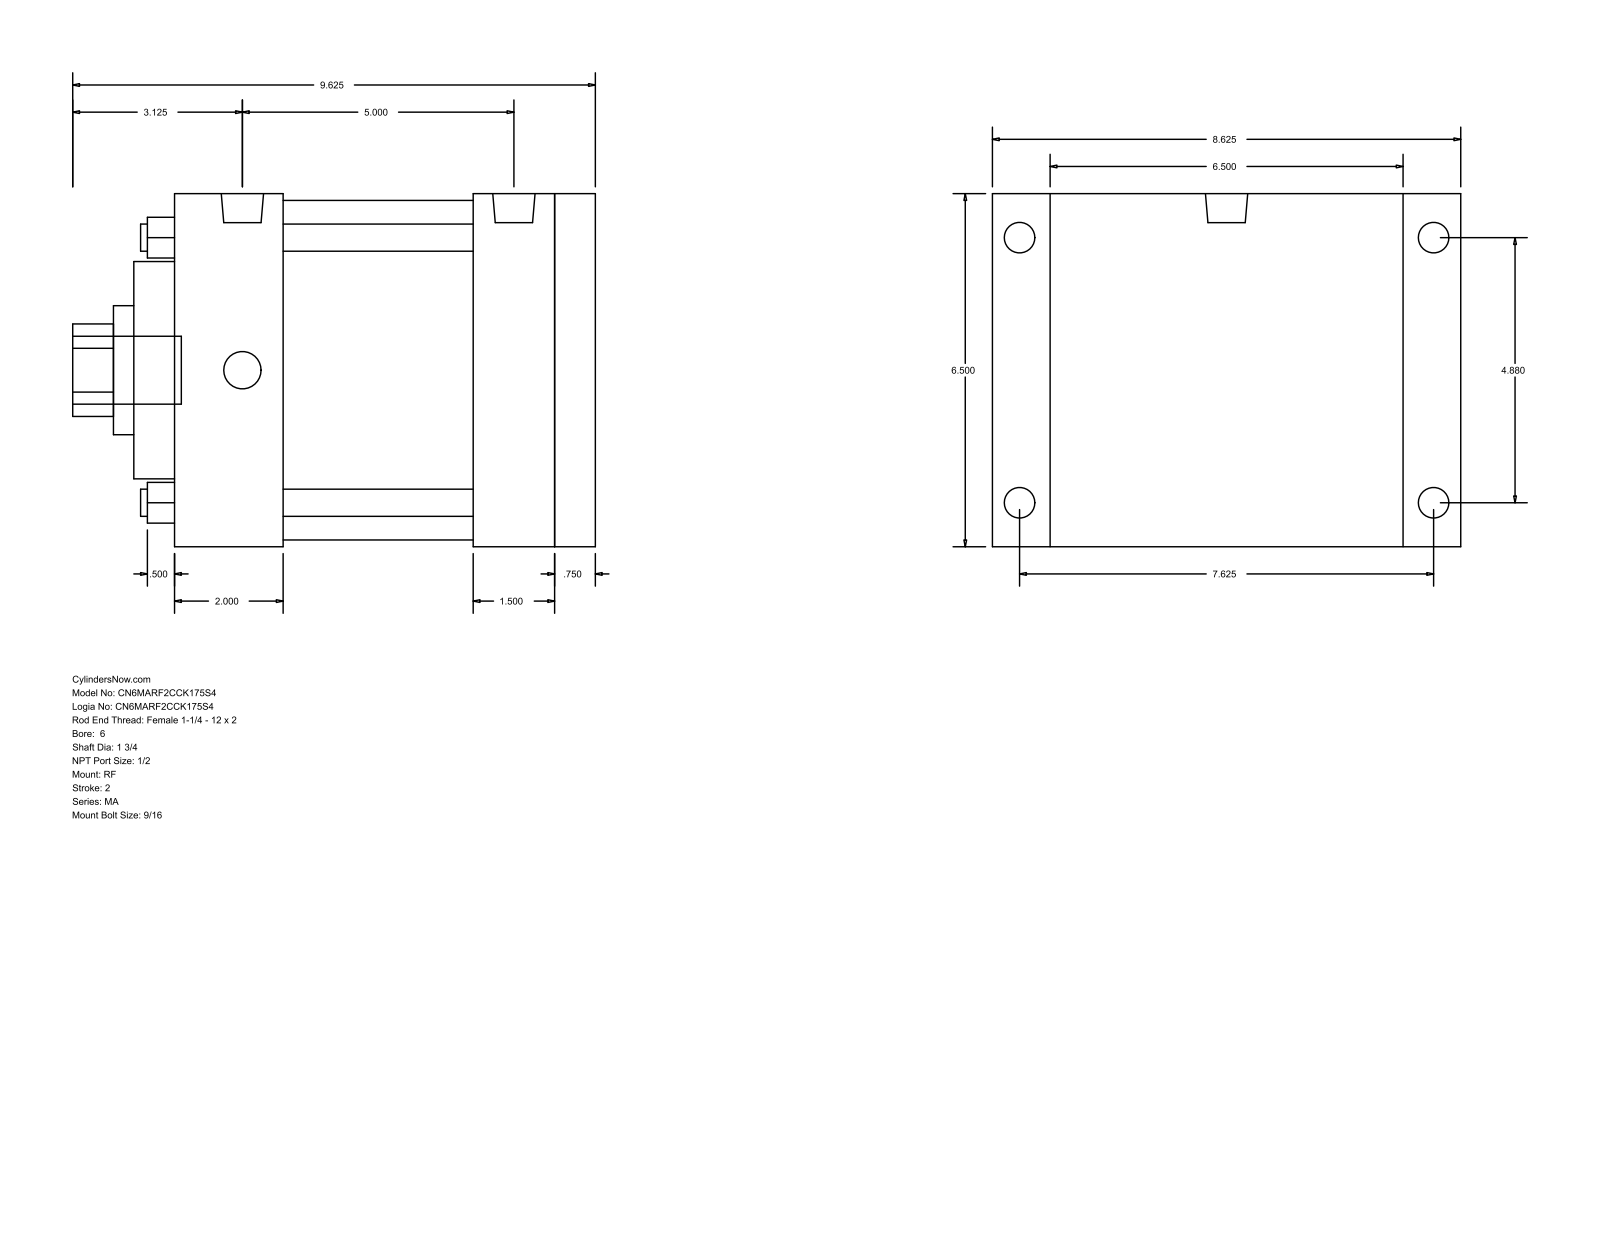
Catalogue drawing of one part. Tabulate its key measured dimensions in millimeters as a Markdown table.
| quantity | value |
| --- | --- |
| part name | MA_RF__0600_1.75 |
| STEP written by | GSSL Pune (CONFIG_CONTROL_DESIGN) |
| units | millimeters |
| bodies | 0 solids, 94 faces (65 planar, 29 cylindrical, 0 other) |
| overall size | 244.47 × 219.07 × 165.1 |
| round holes (diameter × count) | 12.7 × 4, 44.45 × 1, 60.33 × 1, 101.6 × 1, 158.75 × 1 |
| round bosses / shafts (diameter × count) | 17.46 × 4, 14.29 × 4, 19.77 × 2, 31.75 × 1 |
| partial cylindrical surfaces (radius × count) | 21.63 × 1 |
| main face-to-face distances | 165.1, 196.85, 19.04, 177.81, 19.05, 50.8, 127.01, 146.05, 139.7, 88.9 |
| hole center spacings | 87.65, 123.96, 175.31 |
